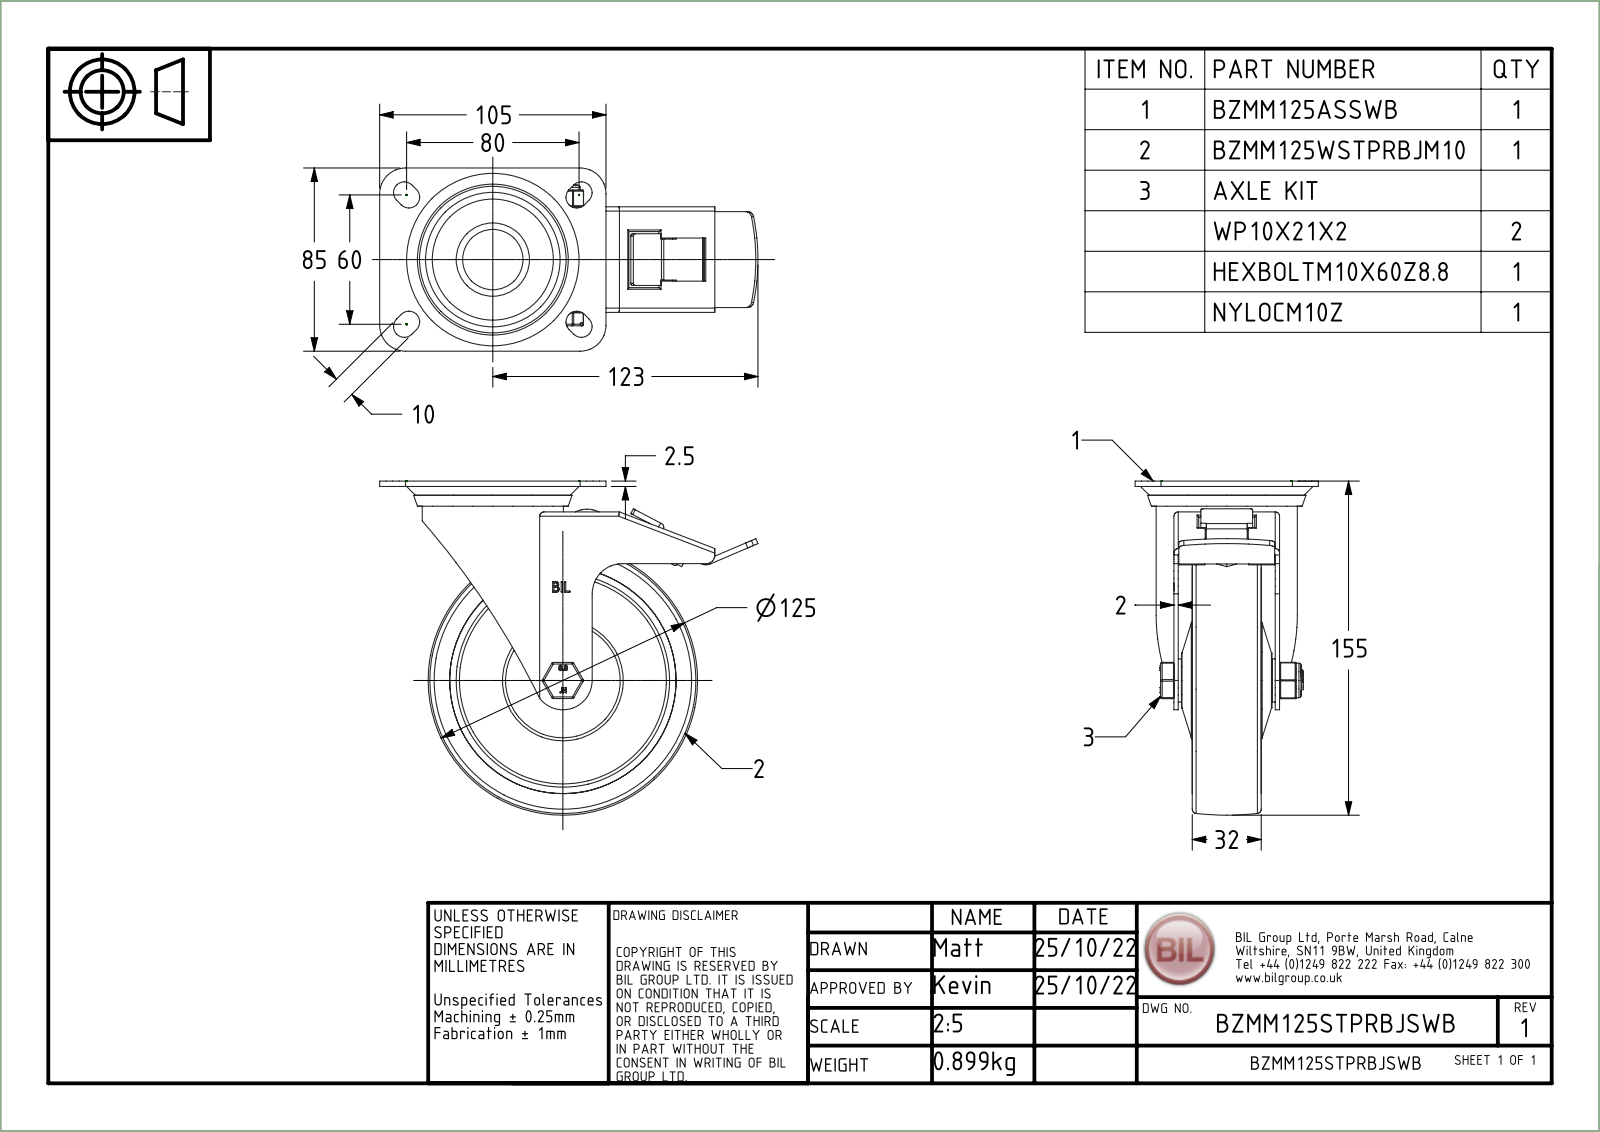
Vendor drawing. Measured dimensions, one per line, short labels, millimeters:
name: BZMM125ASSWB; ZINC PLATED, PRESSED STEEL TOP PLATE; ZINC PLATED, PRESSED STEEL FORKS; BEARING SEAL (+8 more)
written by: Spatial InterOp 3D (AUTOMOTIVE_DESIGN)
unit: mm
bodies: 30 solids, 1290 faces (470 planar, 449 cylindrical, 371 other)
size: 175.5 × 155 × 85
volume: 302 147 mm³; area: 181 895 mm²
holes: 2× ⌀6, 1× ⌀10, 1× ⌀10.2, 1× ⌀10.4, 1× ⌀10.75, 1× ⌀12, 1× ⌀22.5, 1× ⌀28, 1× ⌀30, 1× ⌀31, 1× ⌀32, 1× ⌀32.5
bosses: 1× ⌀65.5, 1× ⌀56, 1× ⌀44.5, 1× ⌀39, 1× ⌀34.5, 1× ⌀34, 1× ⌀30.5, 1× ⌀25.5
rounds: 18× R0.5, 16× R0.75, 12× R1.5, 9× R5, 8× R1, 6× R2, 5× R12, 4× R3
face distances: 2, 5, 13.75, 18.25, 4.5, 8.5, 22.25, 26.75, 40.5, 6.5
hole spacings: 43.75
